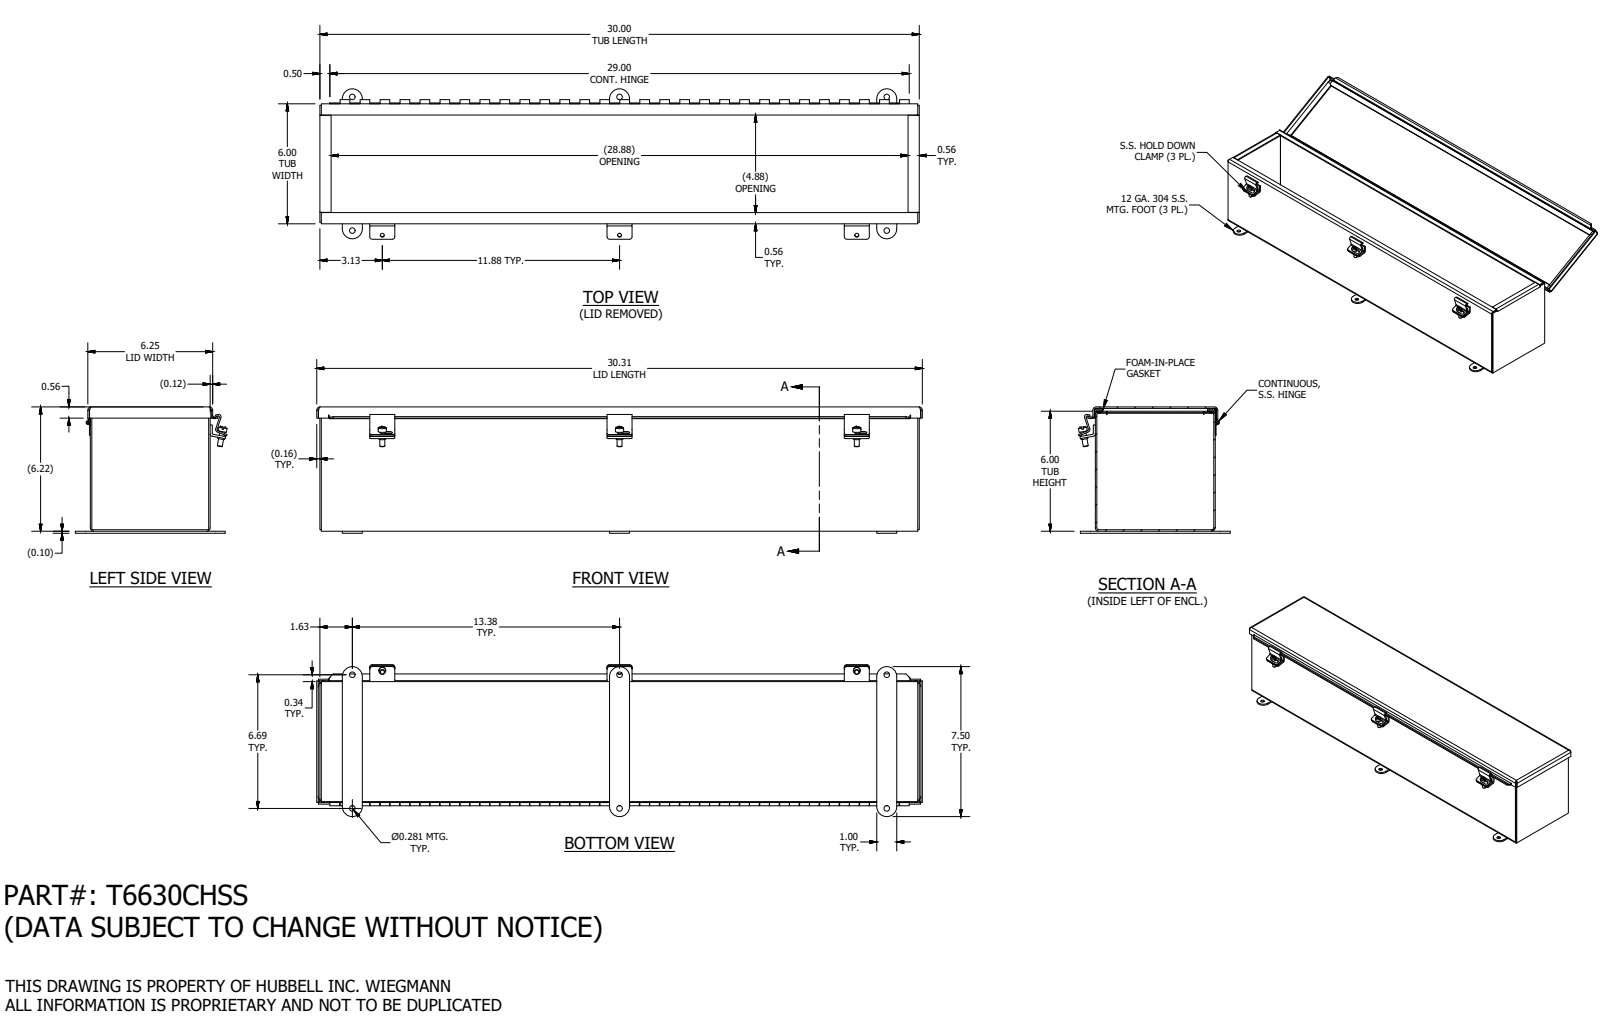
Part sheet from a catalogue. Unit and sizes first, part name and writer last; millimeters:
Units: millimetres
Overall size (bounding box): 770 × 193 × 160.6
Round holes (diameter × count): ⌀2.8 ×6, ⌀7.1 ×6, ⌀5 ×3, ⌀2.9 ×1
Round bosses / shafts (diameter × count): ⌀10.4 ×3, ⌀8.7 ×3, ⌀6.4 ×3, ⌀5.1 ×1, ⌀2.5 ×1
Partial cylindrical surfaces — rounded edges, fillets, slot ends (radius × count): R3.2 ×12, R2.4 ×11, R4.3 ×11, R2.2 ×8, R3.4 ×6, R12.7 ×6, R6.1 ×4, R1.6 ×3
Main face-to-face distances: 1.9, 150.5, 156.1, 152.4, 148.6, 157.9, 154.2, 760.1, 5.5, 153.7
Hole centre spacings: 301.6, 339.7, 379.8, 19.1, 169.8, 301.6, 603.3, 679.5
Volume: 1 229 000 mm³ · Surface area: 1 286 000 mm²
Bodies: 20 solids, 659 faces (395 planar, 225 cylindrical, 39 other)
Part name (STEP PRODUCT): T6630CHSS
STEP written by: SolidWorks 2019 (AUTOMOTIVE_DESIGN)
